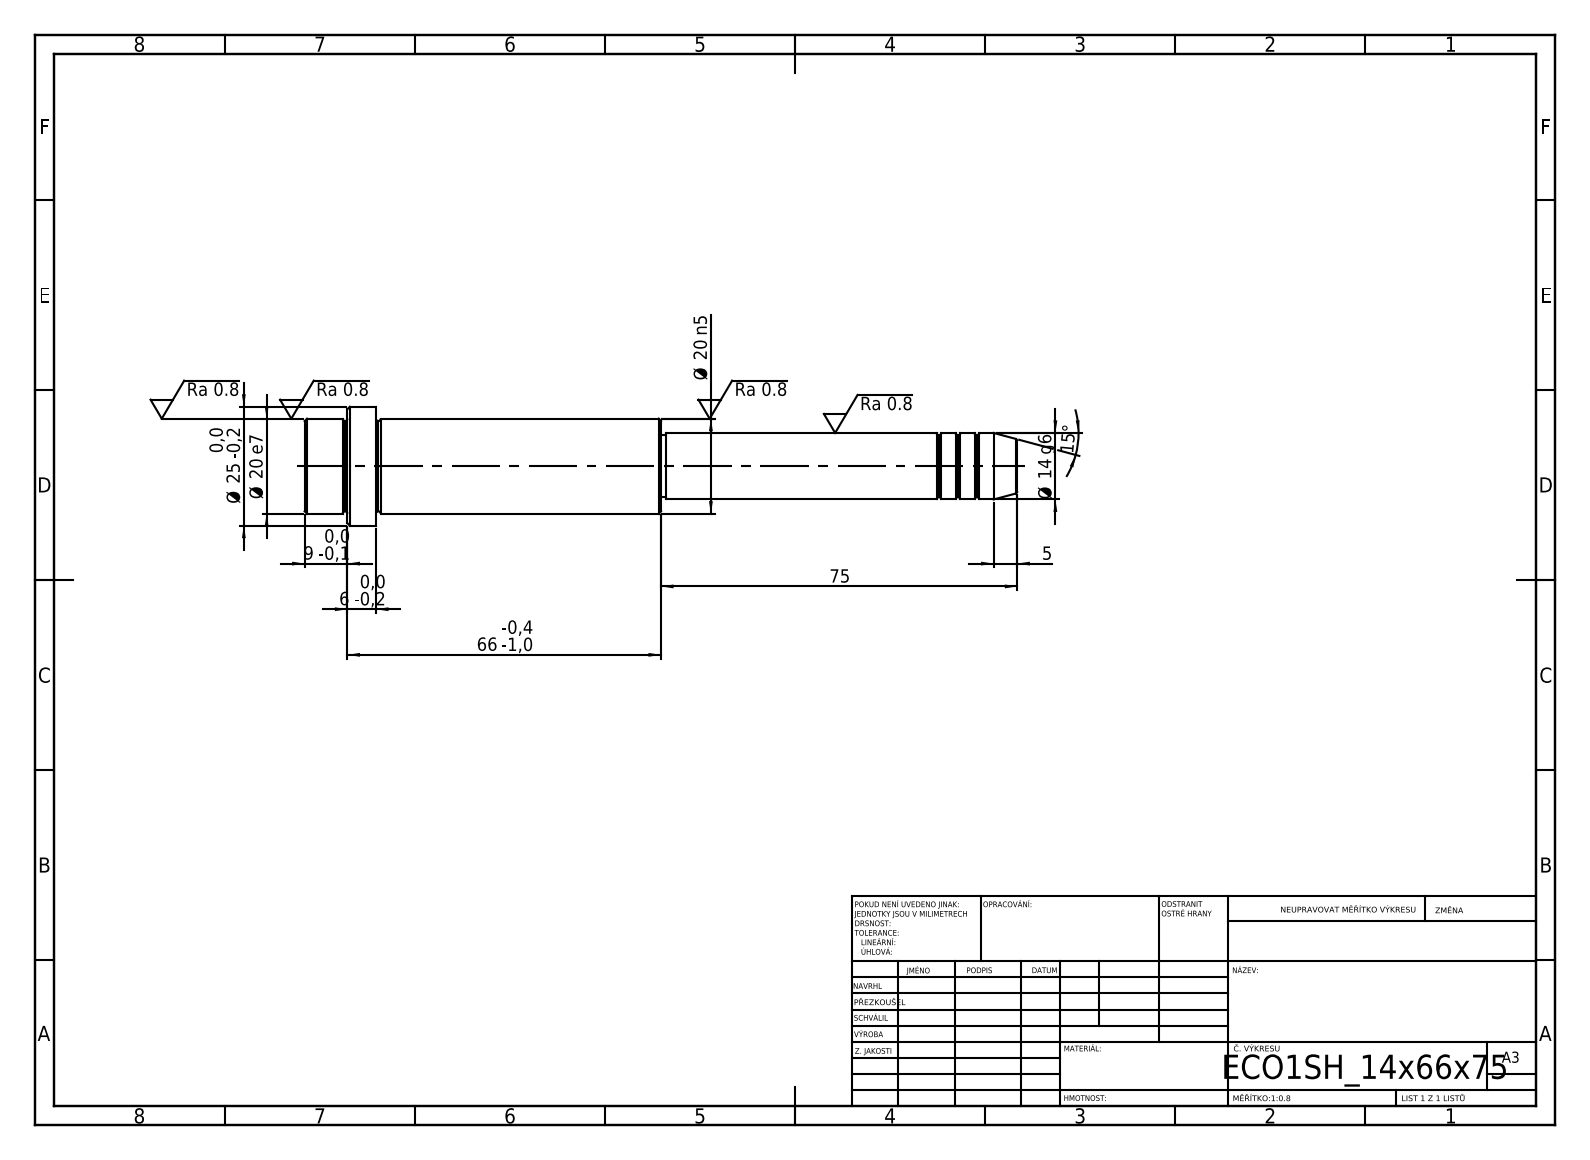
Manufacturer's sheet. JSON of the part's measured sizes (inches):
{"step_written_by": "SolidWorks 2019 (CONFIG_CONTROL_DESIGN)", "units": "inches", "bodies": {"solids": 1, "faces": 52, "planar": 6, "cylindrical": 16, "other": 30}, "overall_size": [5.906, 0.984, 0.984], "volume_in3": 2.19, "surface_area_in2": 14.14, "round_bosses_or_shafts": [[0.984, 1], [0.787, 1], [0.551, 1], [0.512, 1]], "face_to_face_distances": [2.953, 0.591, 2.362, 2.598, 0.236, 0.354, 5.315, 5.551, 5.906, 2.913]}
